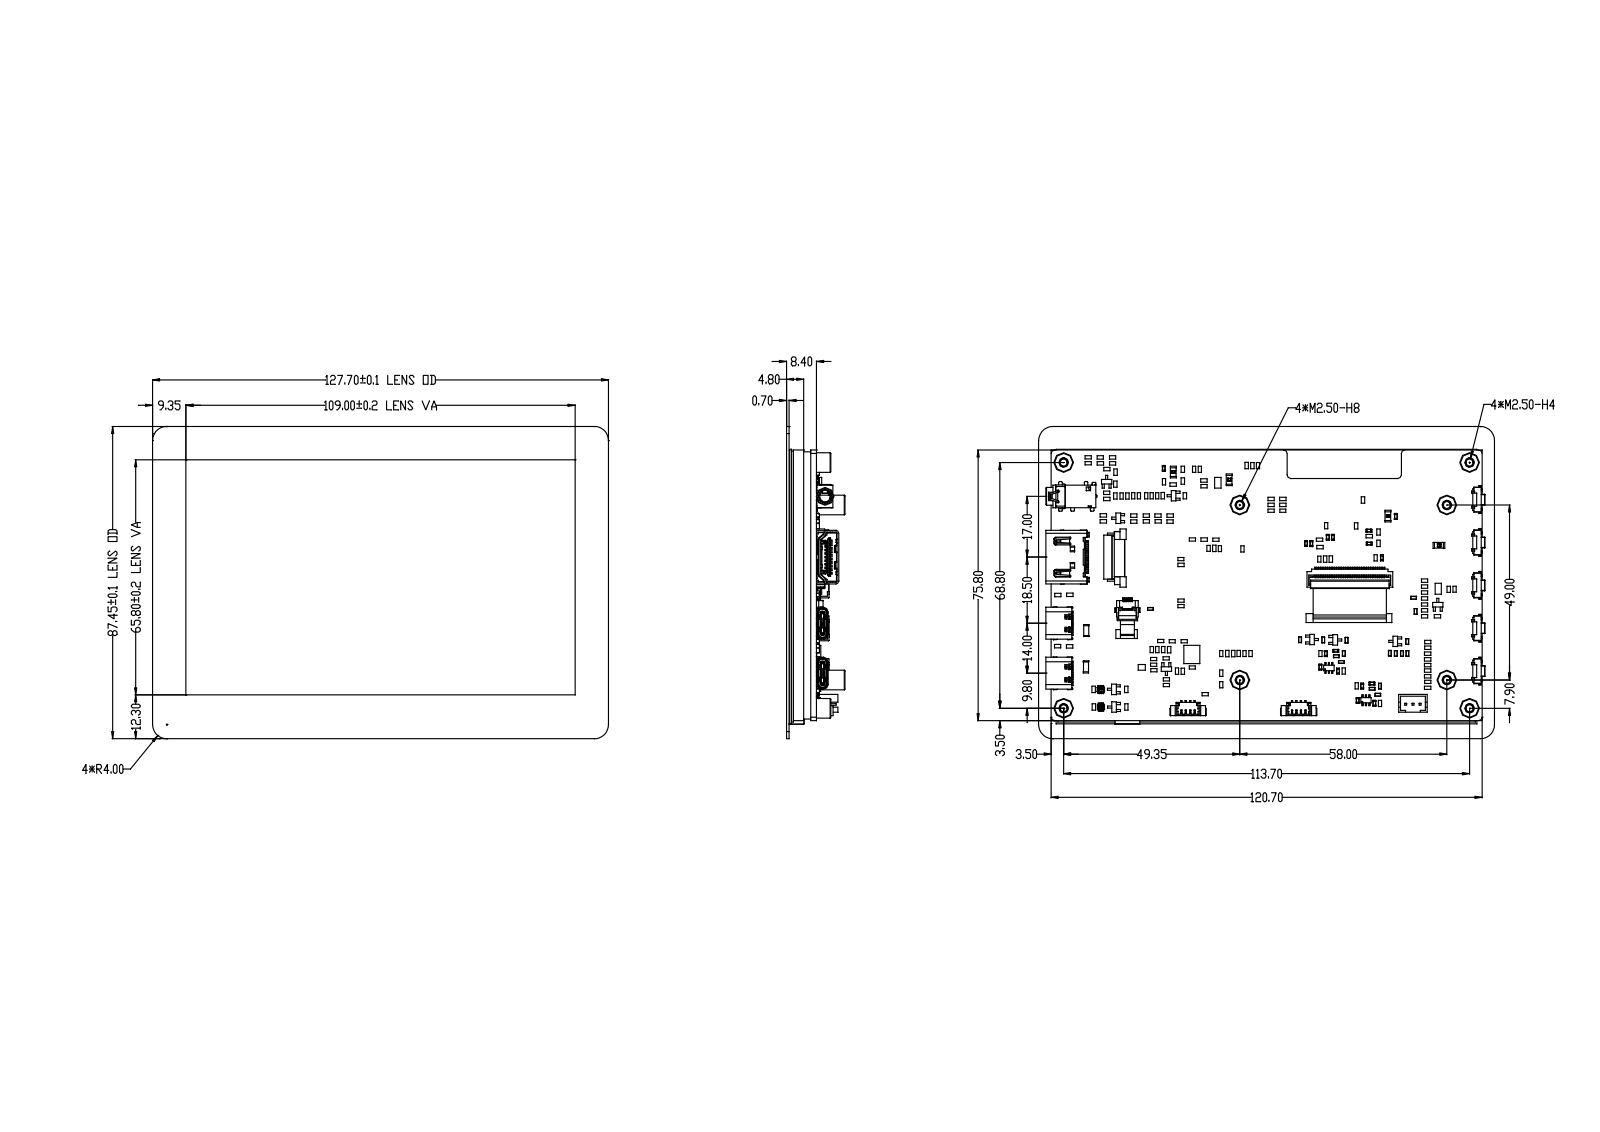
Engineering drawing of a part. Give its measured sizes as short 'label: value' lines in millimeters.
name: 5INCH-1024X600-LCD; 5DP-CAPLCD-TP_B; 5INCH-1024X600-LCD_TP_ASM; SMTSO-M2_5-4ET (+8 more)
written by: CREO PARAMETRIC BY PTC INC, 2021063 (CONFIG_CONTROL_DESIGN)
unit: mm
bodies: 307 solids, 9747 faces (6864 planar, 2205 cylindrical, 678 other)
size: 127.7 × 87.45 × 16.4
volume: 62 538 mm³; area: 80 434 mm²
holes: 13× ⌀0.8, 8× ⌀2.5, 8× ⌀4.3, 5× ⌀1, 4× ⌀0.76, 2× ⌀0.22, 2× ⌀1.4, 1× ⌀3.6
bosses: 10× ⌀0.6, 8× ⌀5.5, 8× ⌀4.19, 4× ⌀0.5, 2× ⌀1.3, 2× ⌀0.71, 1× ⌀5
rounds: 184× R0.1, 77× R0.2, 73× R0.15, 63× R0.25, 39× R0.4, 38× R0.3, 23× R0.5, 21× R0.35
face distances: 2, 1.9, 1.6, 3.6, 4.85, 7, 5.4, 3.4, 4.75, 2.85
hole spacings: 2.3, 2, 2.95, 3.35, 3.82, 5.78, 6.26, 8.05
